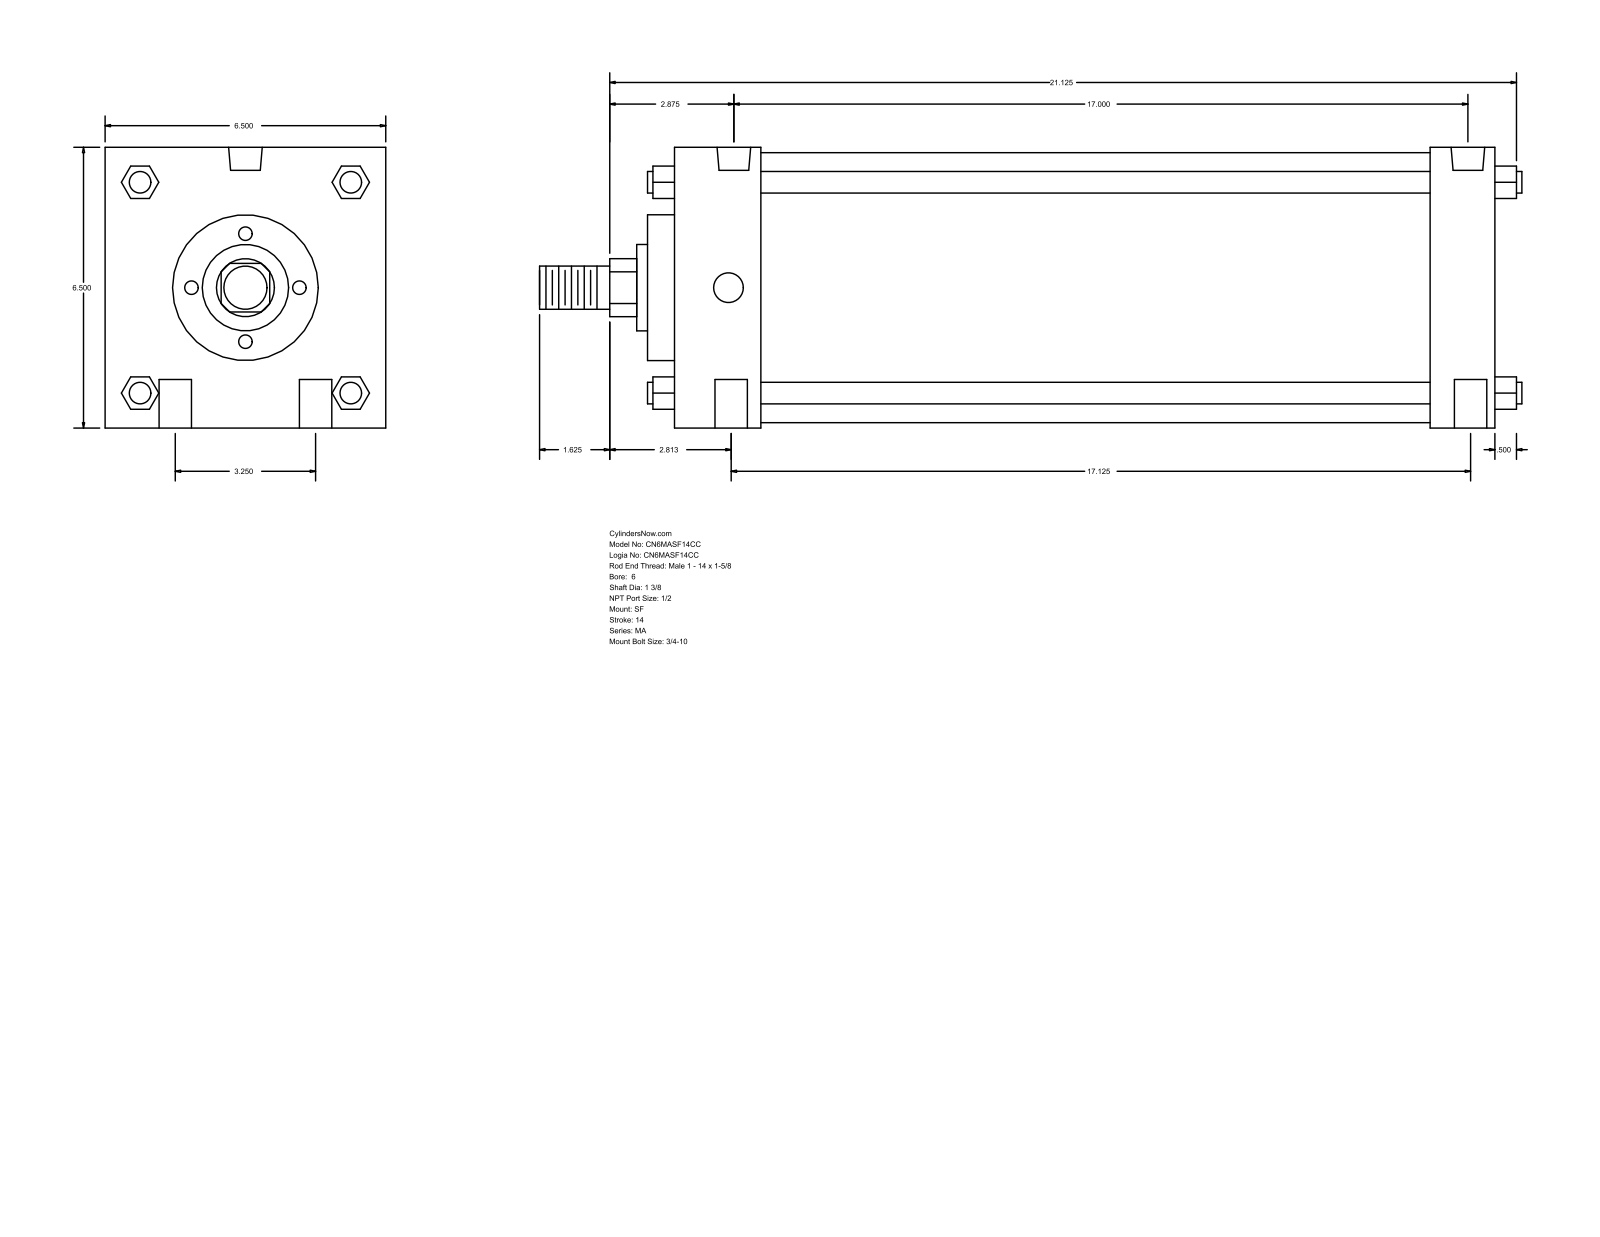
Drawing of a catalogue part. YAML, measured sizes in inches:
part_name: "MA_SF__0600_1.375"
step_written_by: "GSSL Pune (CONFIG_CONTROL_DESIGN)"
units: inches
bodies: {solids: 0, faces: 126, planar: 95, cylindrical: 31, other: 0}
overall_size: [22.75, 6.5, 6.5]
round_holes:
  - {diameter: 0.75, count: 4}
  - {diameter: 0.687, count: 2}
  - {diameter: 0.778, count: 2}
round_bosses_or_shafts:
  - {diameter: 0.5, count: 4}
  - {diameter: 6.25, count: 1}
  - {diameter: 3.375, count: 1}
  - {diameter: 2, count: 1}
  - {diameter: 1.375, count: 1}
  - {diameter: 1, count: 1}
partial_cylinders:
  - {radius: 0.672, count: 1}
face_to_face_distances: [6.5, 19, 17.5, 2, 1.5, 15.5, 17, 2.625, 0.625, 18.125]
hole_center_spacings: [1.626, 17.139, 3.25, 17.125, 17.43, 17, 17]
